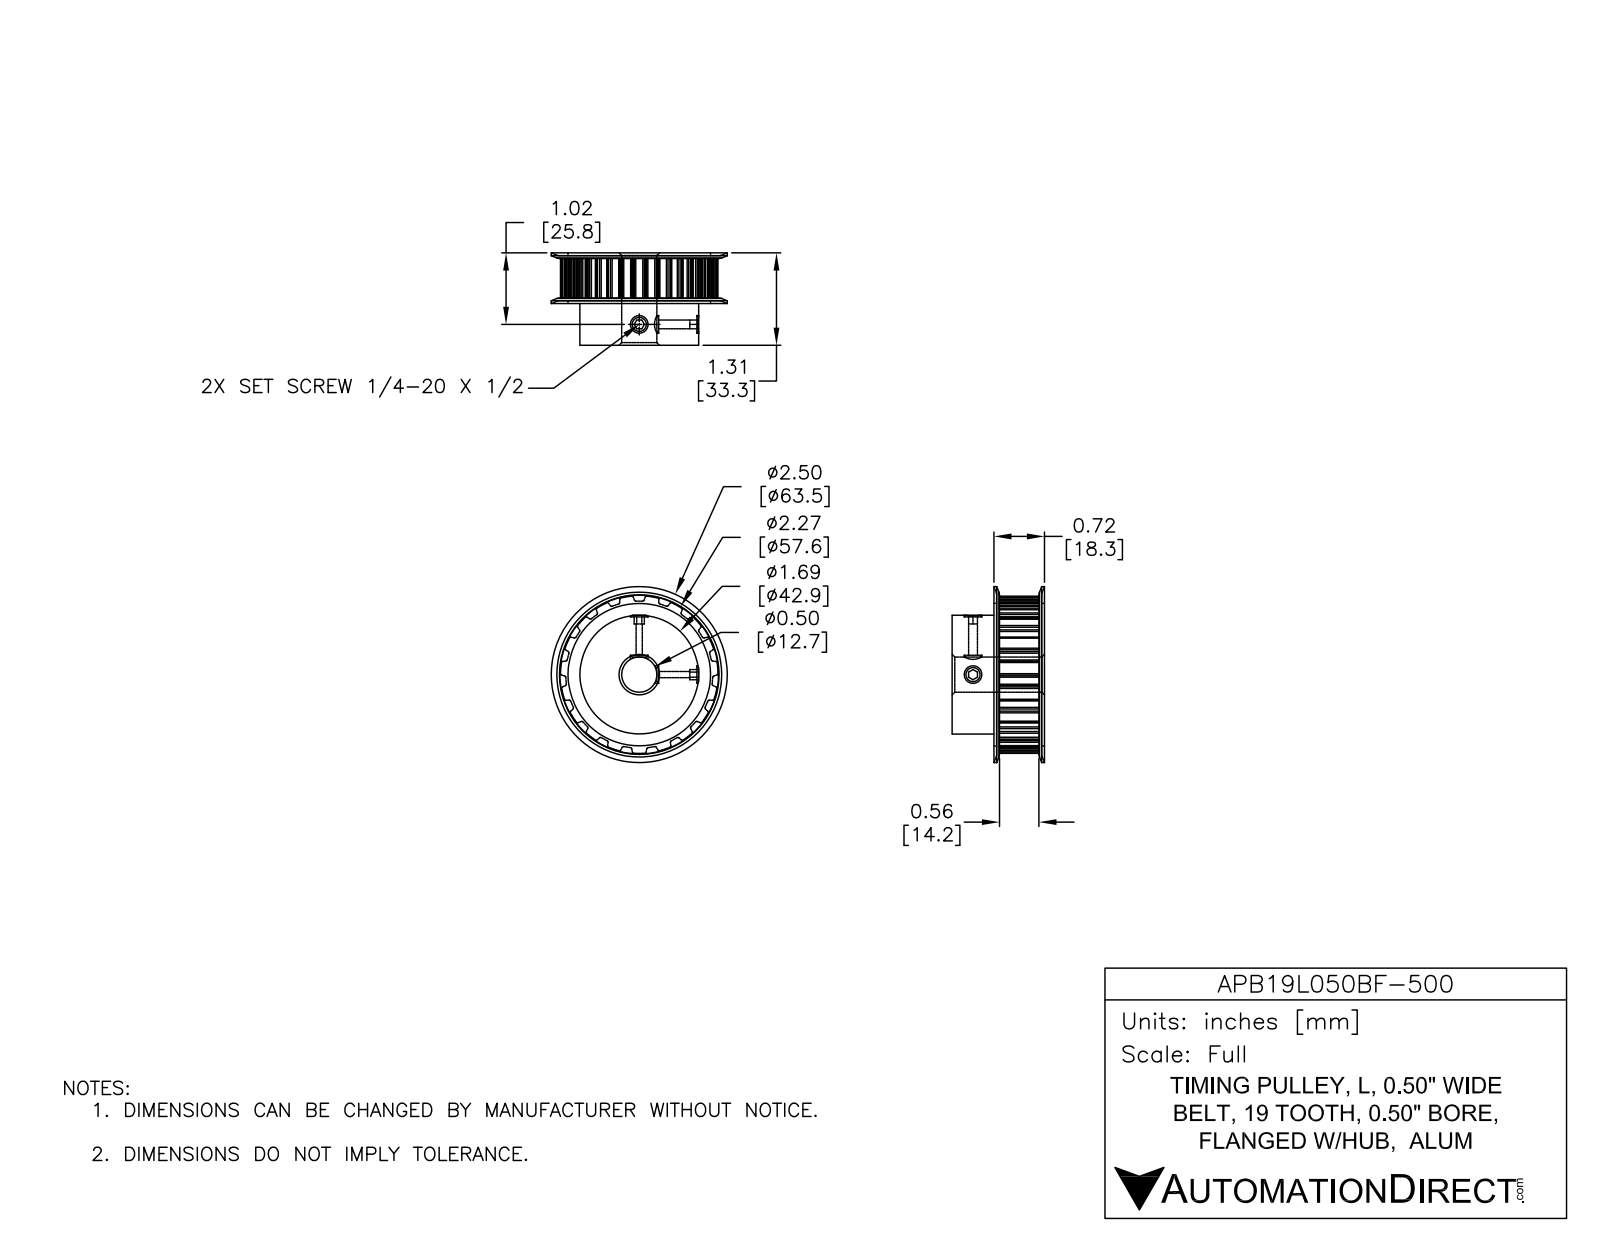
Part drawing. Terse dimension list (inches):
name: APB19L050BF-500
written by: SolidWorks 2014 (AUTOMOTIVE_DESIGN)
unit: in
bodies: 1 solid, 160 faces (63 planar, 75 cylindrical, 22 other)
size: 2.5 × 2.5 × 1.313
volume: 3.799 in³; area: 22.63 in²
holes: 2× ⌀0.088, 1× ⌀0.5
bosses: 1× ⌀1.688
rounds: 38× R0.015, 1× R1.064
face distances: 1.313, 0.68, 0.633, 0.04, 0.64, 1.273, 0.04, 0.6, 0.08, 1.233
